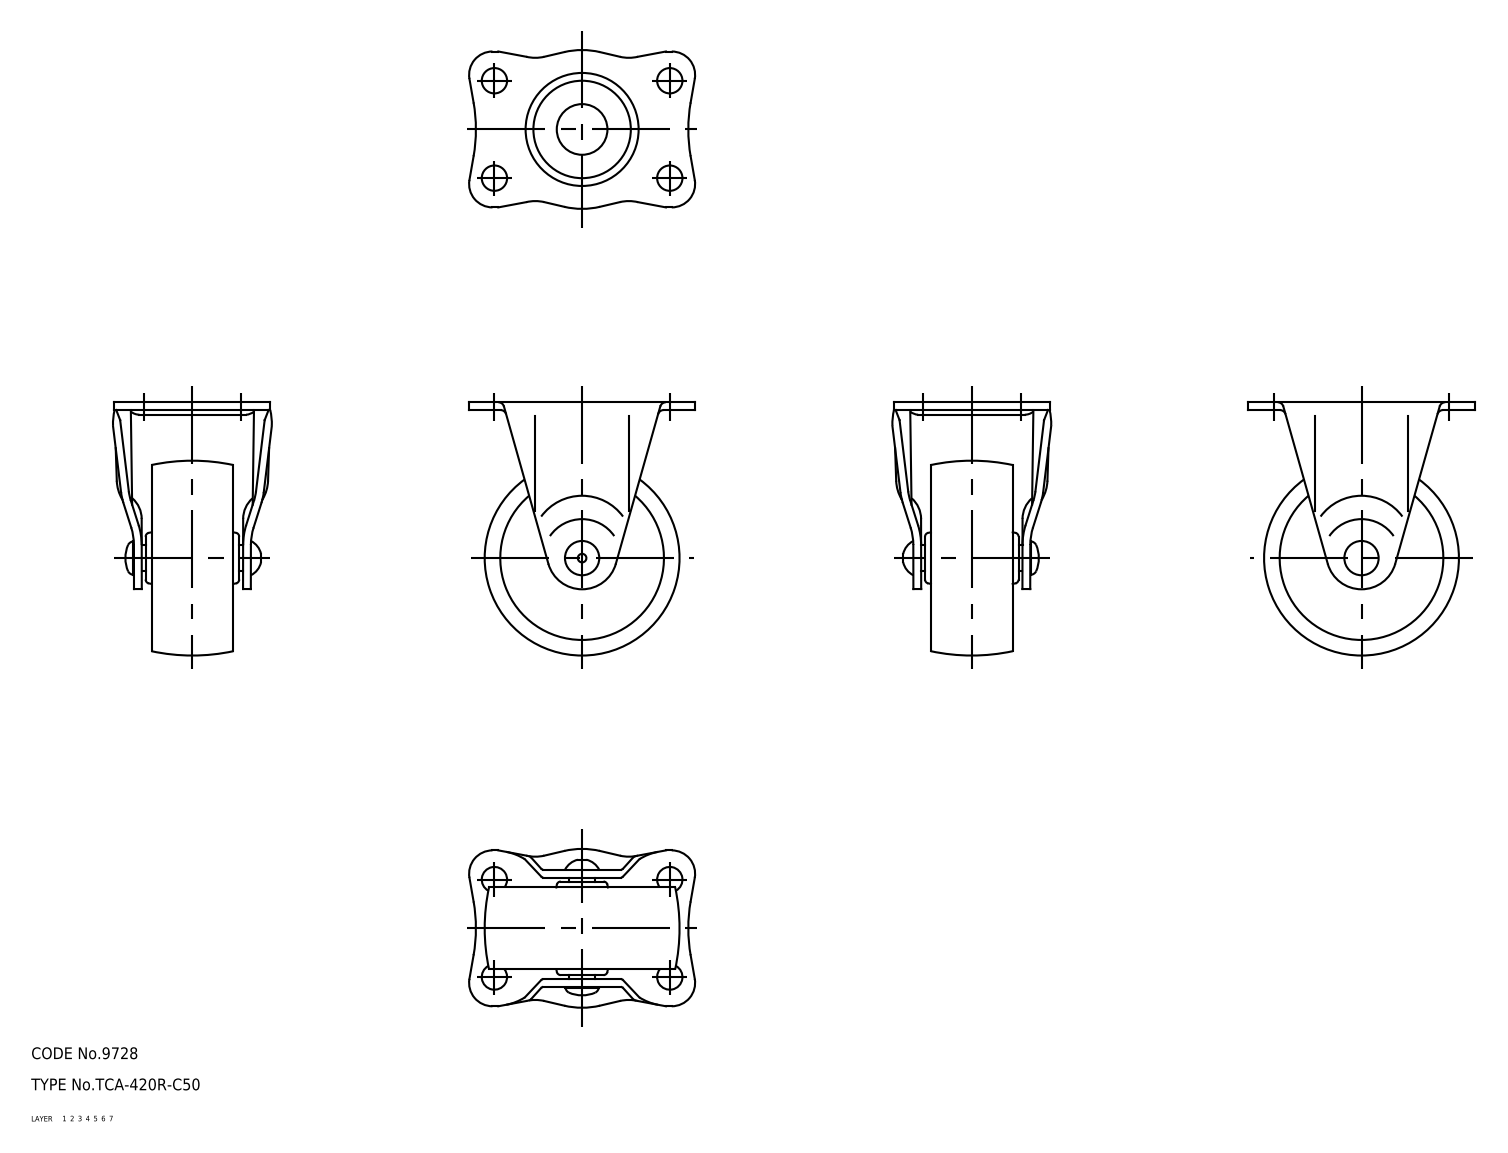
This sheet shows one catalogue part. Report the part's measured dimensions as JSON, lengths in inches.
{"part_name": "wheel; axle; No_420_R_C50_4_103_36", "step_written_by": "CADfix (AUTOMOTIVE_DESIGN)", "units": "inches", "bodies": {"solids": 3, "faces": 181, "planar": 0, "cylindrical": 0, "other": 181}, "overall_size": [2.559, 2.283, 1.575], "volume_in3": 2.273, "surface_area_in2": 30.16}
